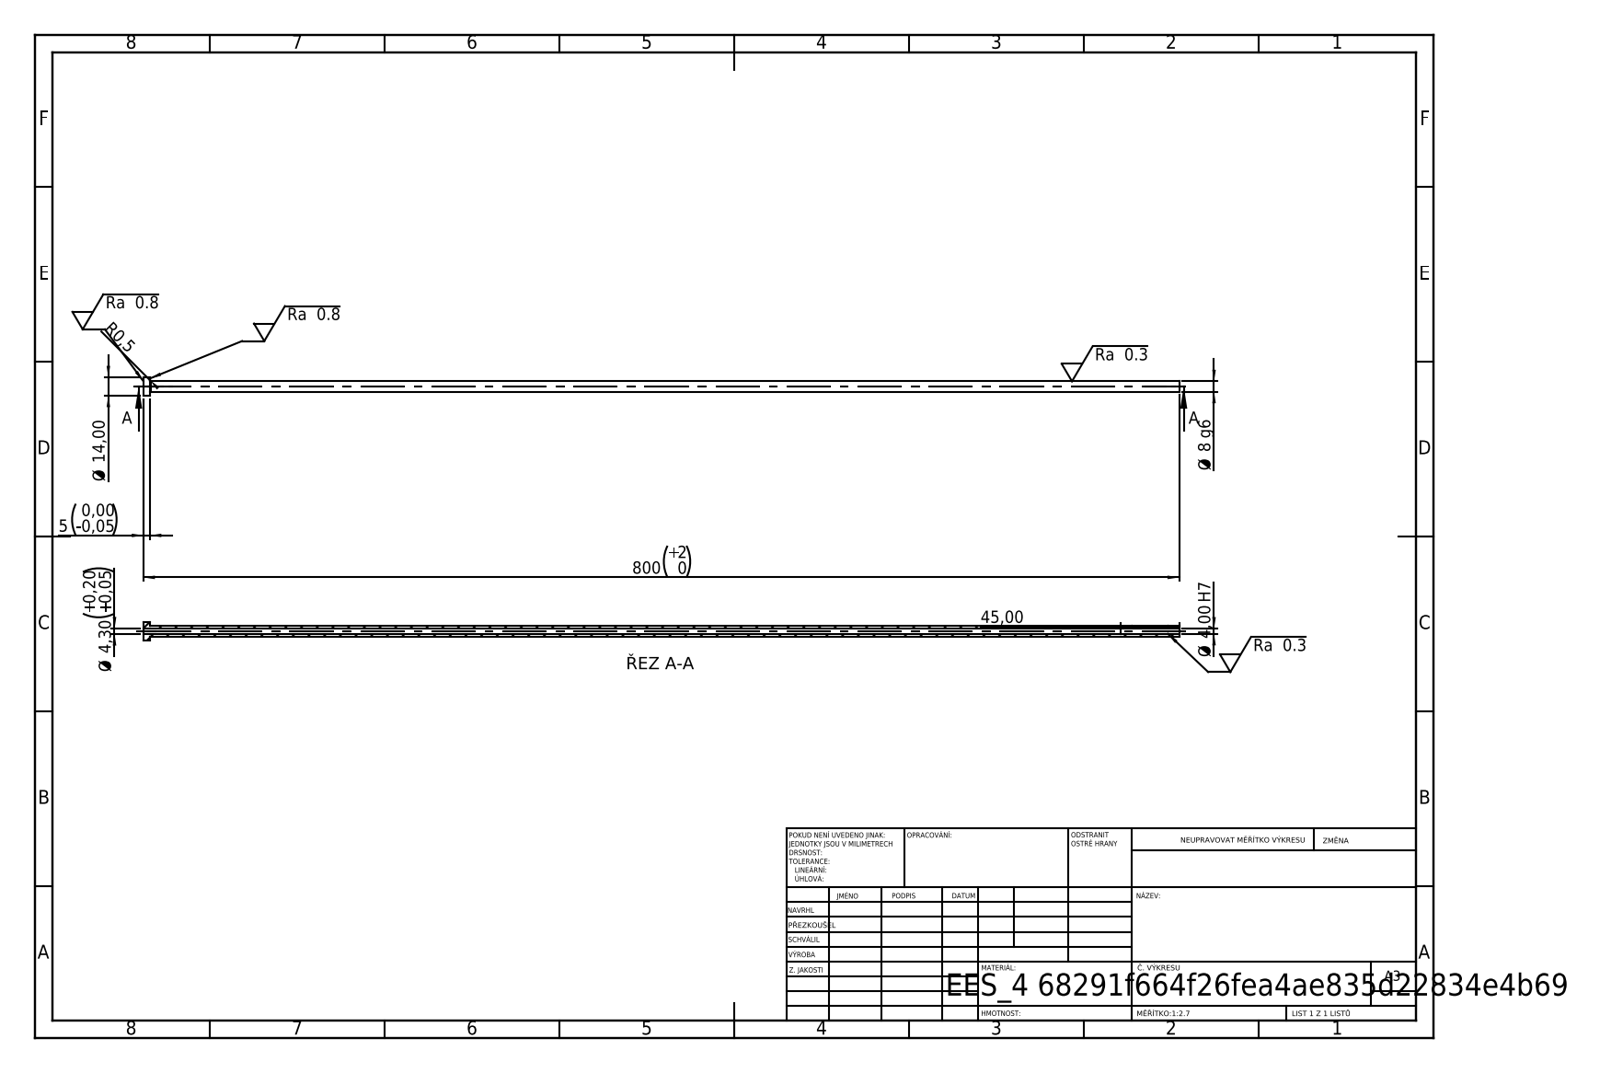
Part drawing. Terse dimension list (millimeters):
written by: SolidWorks 2019 (CONFIG_CONTROL_DESIGN)
unit: mm
bodies: 1 solid, 14 faces (4 planar, 8 cylindrical, 2 other)
size: 800 × 14 × 14
volume: 29 203 mm³; area: 31 243 mm²
holes: 1× ⌀4, 1× ⌀4.3
bosses: 1× ⌀14, 1× ⌀8
face distances: 5, 800, 795, 755, 750, 45
